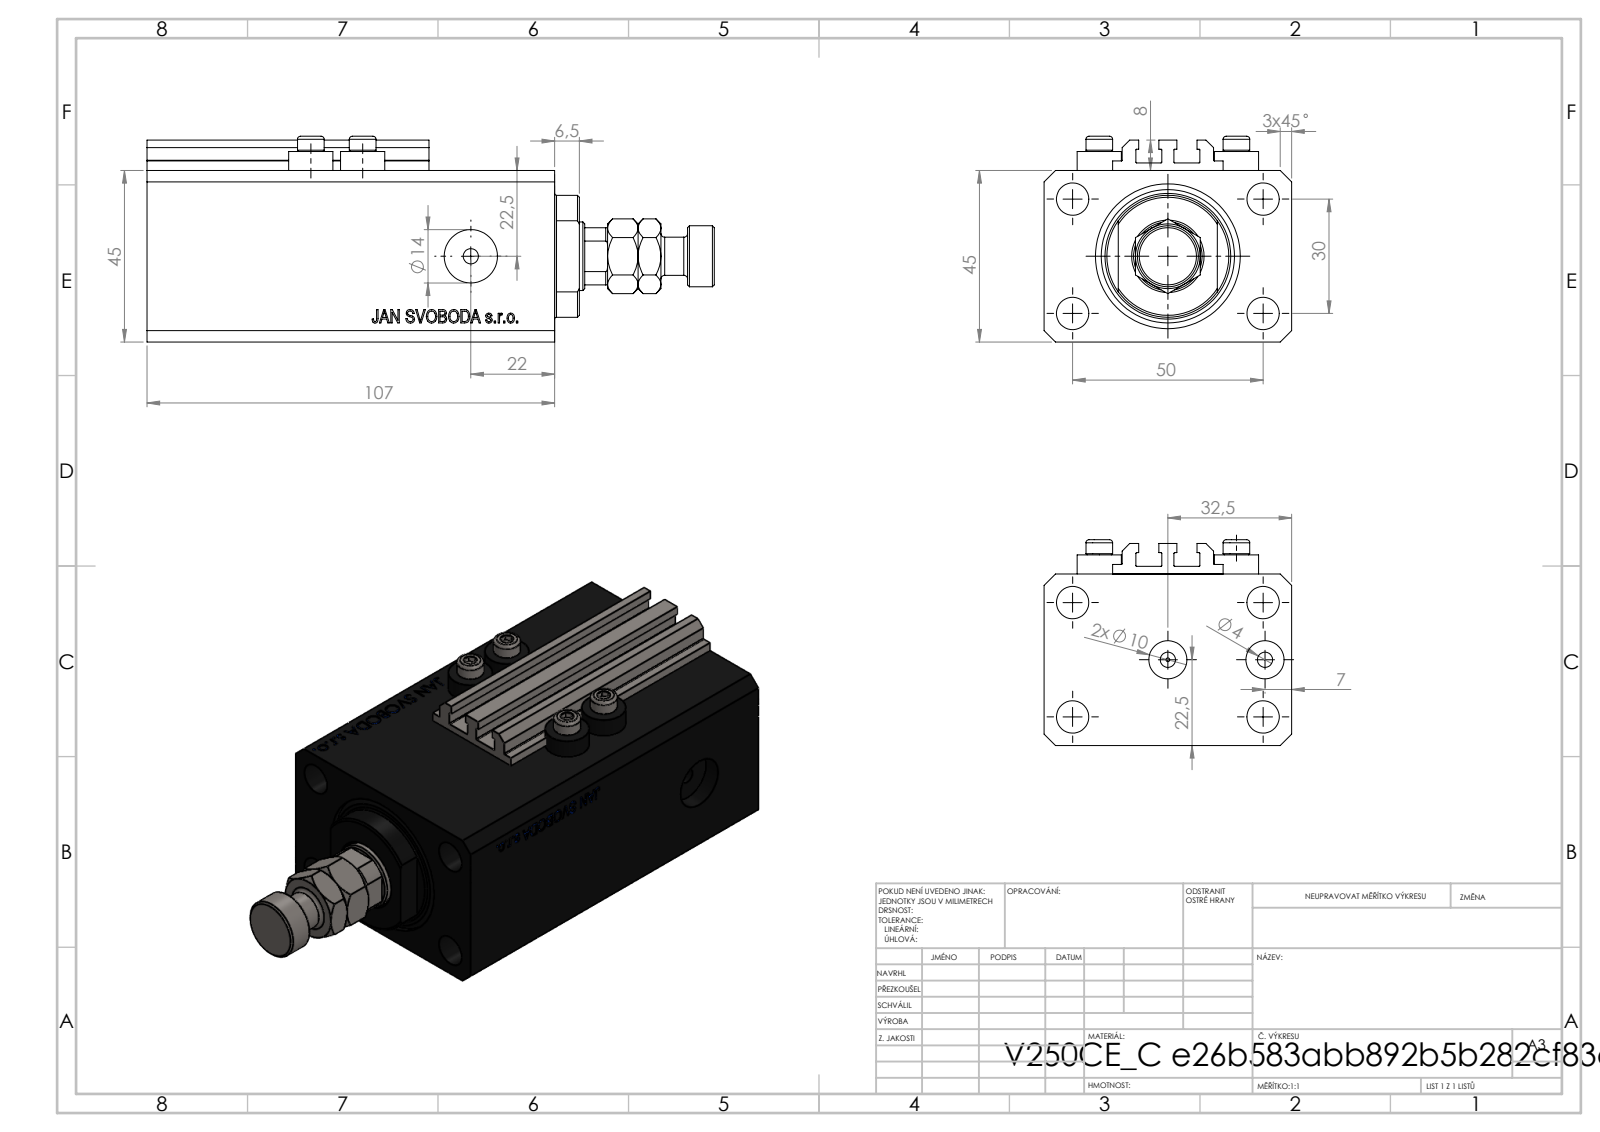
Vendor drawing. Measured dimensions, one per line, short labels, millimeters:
name: MFA; V250CE_VC_C; V250CE_C_Body; ALLEN BOLT V250CE (+1 more)
written by: SolidWorks 2019 (CONFIG_CONTROL_DESIGN)
unit: mm
bodies: 9 solids, 1090 faces (520 planar, 92 cylindrical, 478 other)
size: 149 × 65 × 54
volume: 293 978 mm³; area: 76 479 mm²
holes: 8× ⌀4, 5× ⌀8.5, 2× ⌀10, 2× ⌀14, 1× ⌀1.25, 1× ⌀18, 1× ⌀25, 1× ⌀38
bosses: 4× ⌀11.6, 4× ⌀7, 1× ⌀16
rounds: 10× R0.2, 1× R8.5, 1× R16
face distances: 45, 65, 14, 107, 93, 47, 6.9, 20.5, 2.5, 6
hole spacings: 29.15, 13.6, 15.01, 30, 36, 38.48, 50, 52.68
